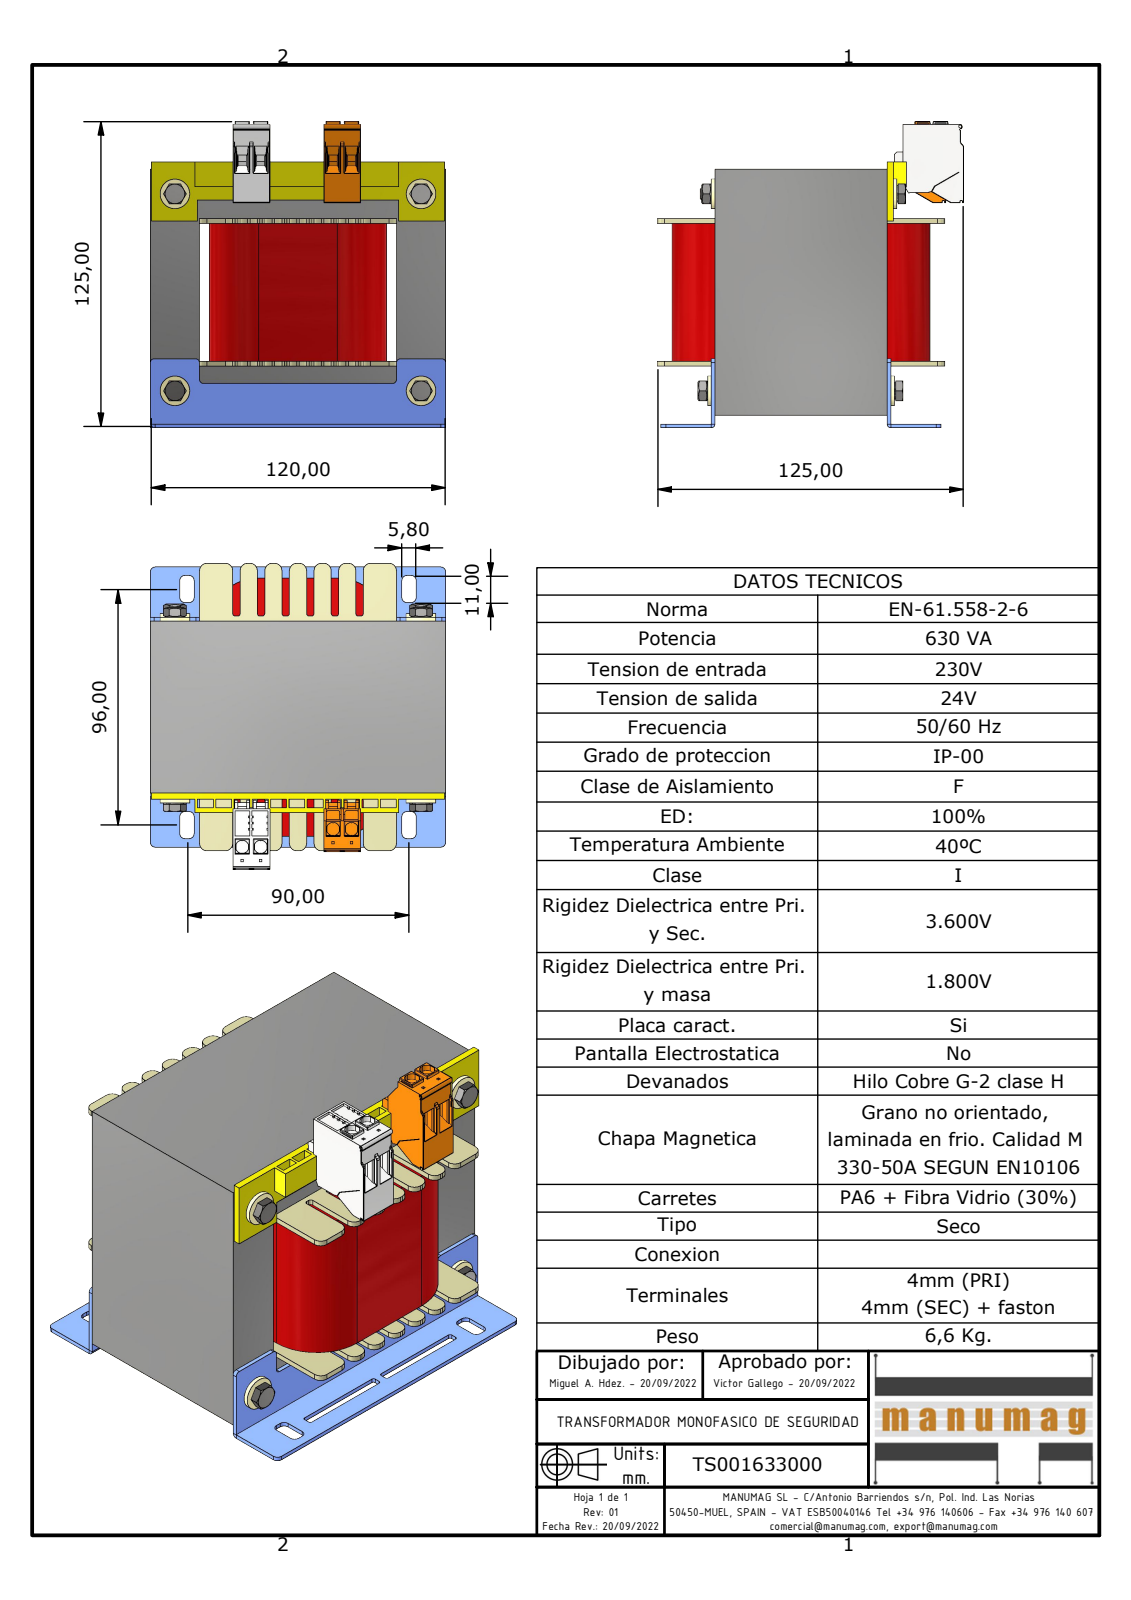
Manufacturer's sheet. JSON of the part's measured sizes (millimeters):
{"part_name": "TS001633000; EI120 x 100 - 70 (Rc40); AF40DIN; EI120 (+6 more)", "step_written_by": "Autodesk Inventor 2023 (AUTOMOTIVE_DESIGN)", "units": "millimeters", "bodies": {"solids": 23, "faces": 3908, "planar": 3099, "cylindrical": 566, "other": 243}, "overall_size": [124.65, 124.5, 120], "volume_mm3": 975529, "surface_area_mm2": 178655, "round_holes": [[4.13, 4], [5, 4], [6.6, 4], [6.8, 2]], "round_bosses_or_shafts": [[12, 4], [6.7, 4], [5.9, 4], [4.57, 4]], "partial_cylinders_radius": [[0.15, 163], [0.2, 58], [1, 32], [3, 28], [2, 20], [0.8, 18], [0.5, 14], [0.3, 12]], "face_to_face_distances": [80, 20, 40, 60, 100, 70, 16, 1.5, 56, 4], "hole_center_spacings": [80, 100, 128.06]}
